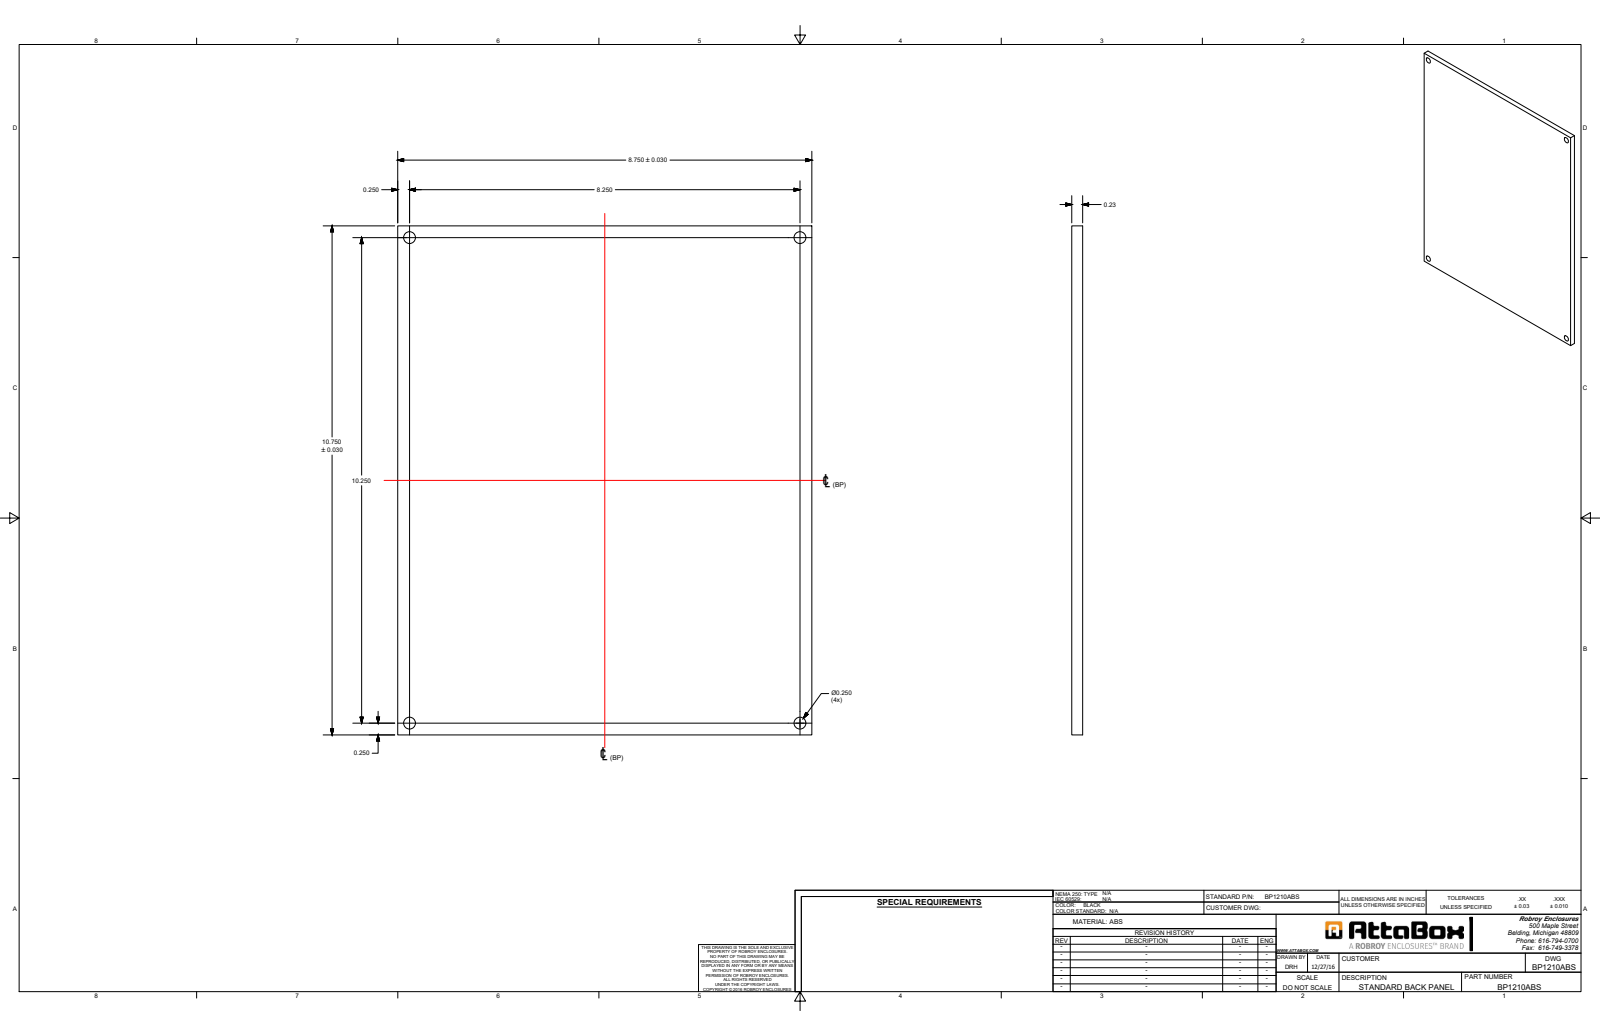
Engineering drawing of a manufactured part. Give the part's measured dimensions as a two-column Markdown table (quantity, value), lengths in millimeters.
| quantity | value |
| --- | --- |
| part name | BP1210ABS_Default |
| STEP written by | SolidWorks 2023 (CONFIG_CONTROL_DESIGN) |
| units | millimeters |
| bodies | 1 solid, 10 faces (6 planar, 4 cylindrical, 0 other) |
| overall size | 273.1 × 222.3 × 5.8 |
| volume | 353 800 mm³ |
| surface area | 127 400 mm² |
| round holes (diameter × count) | 6.4 × 4 |
| main face-to-face distances | 5.8, 222.3, 273.1 |
| hole center spacings | 209.6, 260.4, 334.2 |
